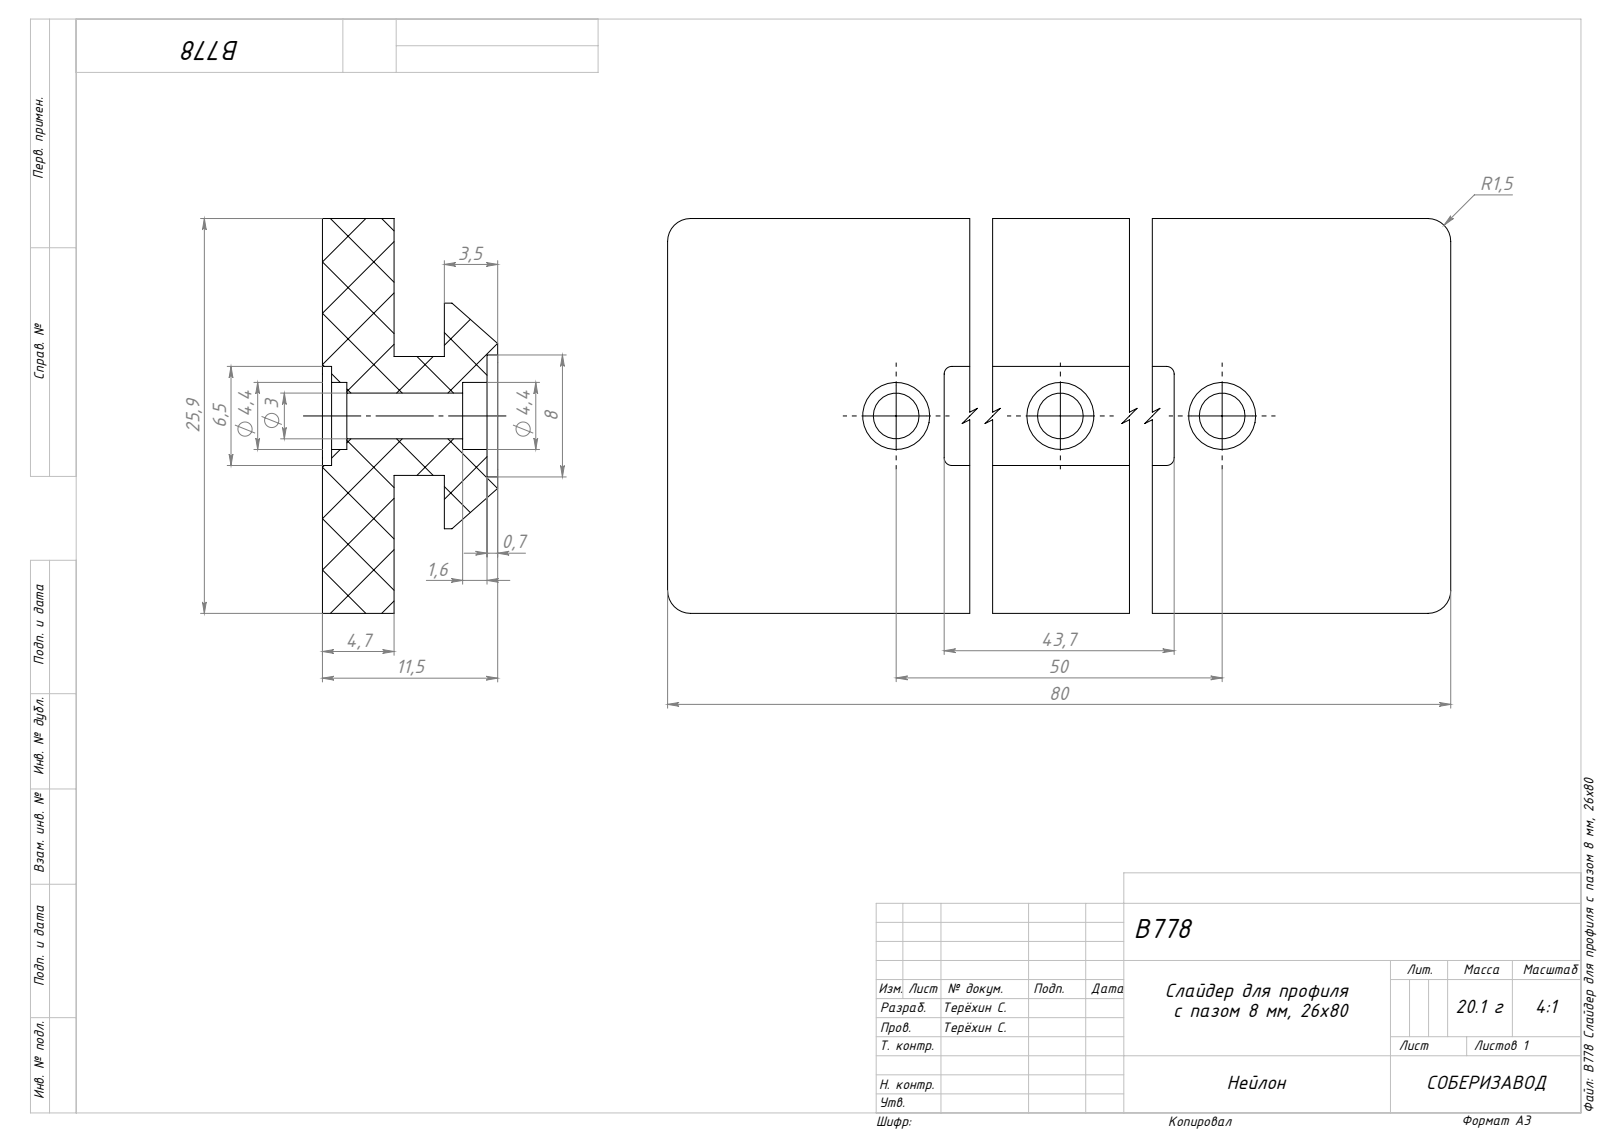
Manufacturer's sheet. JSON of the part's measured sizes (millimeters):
{"part_name": "B778 Слайдер для профиля с пазом 8 мм, 26х80_00; B778 Слайдер для профиля с пазом 8 мм, 26х80", "step_written_by": "SolidWorks 2025 (CONFIG_CONTROL_DESIGN)", "units": "millimeters", "bodies": {"solids": 1, "faces": 68, "planar": 34, "cylindrical": 34, "other": 0}, "overall_size": [80, 25.9, 11.5], "volume_mm3": 14048, "surface_area_mm2": 7970, "round_holes": [[3, 3], [4.4, 3], [4.8, 2]], "partial_cylinders_radius": [[0.5, 8], [1.5, 4]], "face_to_face_distances": [4.7, 8, 3.3, 10.8, 6.1, 2.8, 9.05, 16.85, 25.9, 10.2], "hole_center_spacings": [12.5, 25, 37.5, 50]}
